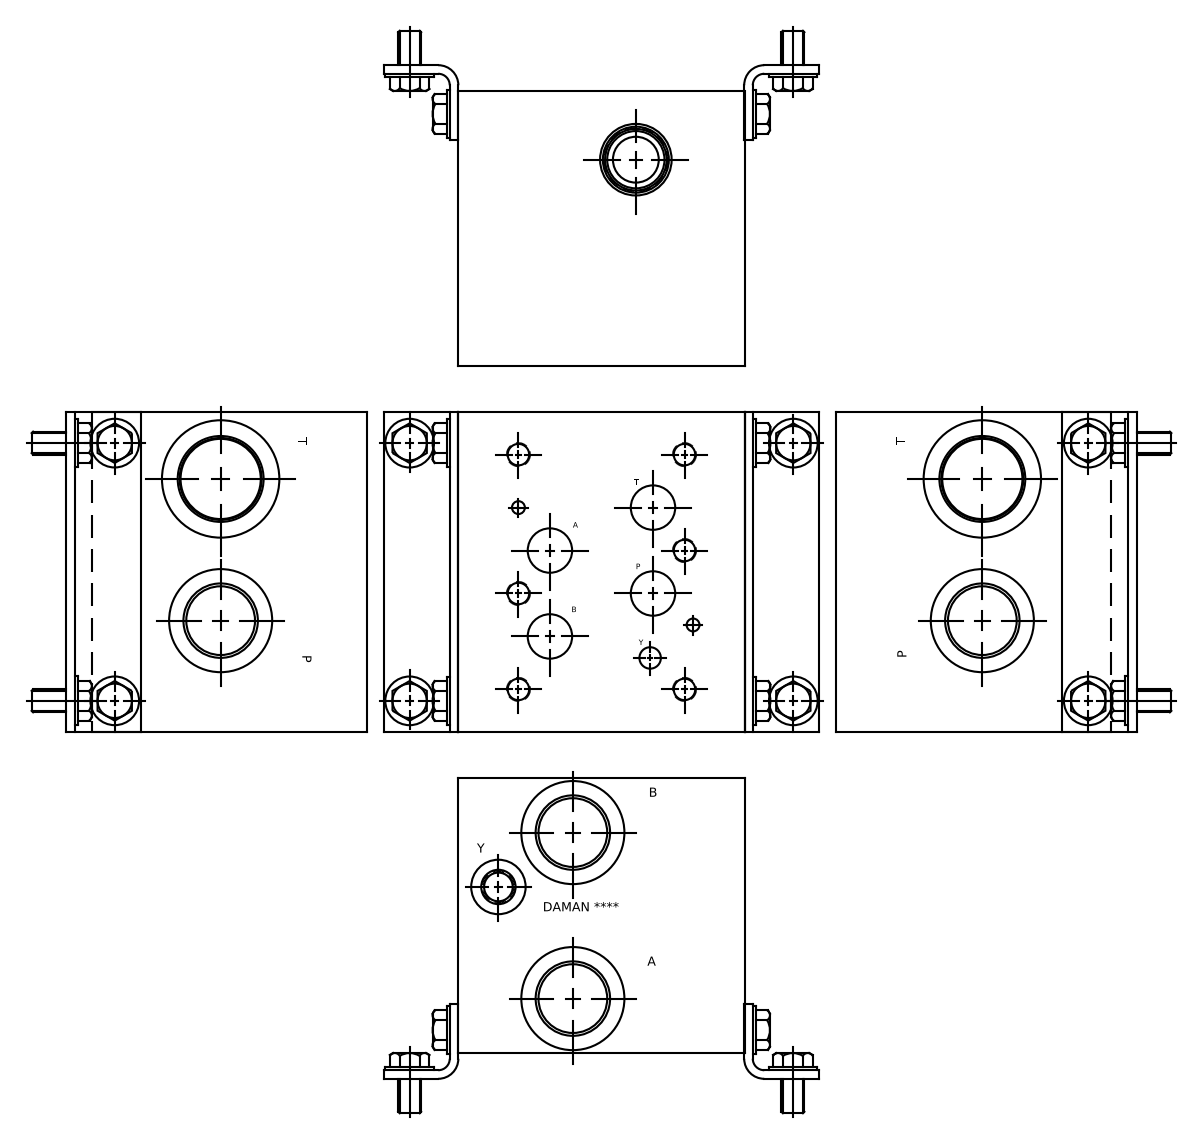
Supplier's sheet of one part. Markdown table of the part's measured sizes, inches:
| quantity | value |
| --- | --- |
| part name | Part_AD08HP015S_S_3D |
| STEP written by | Autodesk Inventor 2020 (AUTOMOTIVE_DESIGN) |
| units | inches |
| bodies | 1 solid, 594 faces (335 planar, 68 cylindrical, 191 other) |
| overall size | 7 × 6.25 × 6 |
| volume | 234.1 in³ |
| surface area | 331.3 in² |
| round holes (diameter × count) | 0.422 × 8, 0.5 × 8, 0.969 × 4, 1.544 × 3, 2.306 × 3, 0.281 × 2, 1.453 × 2, 1.625 × 2, 1.625 × 2, 1.644 × 2, 1.713 × 2, 0.437 × 1 |
| main face-to-face distances | 6, 6.25, 7, 0.031, 6.219, 6.969, 6.188, 0.75, 0.781, 5.469 |
| hole center spacings | 1.163, 1.163, 1.875, 2.094, 2.438, 2.938, 3.607, 4.221 |
